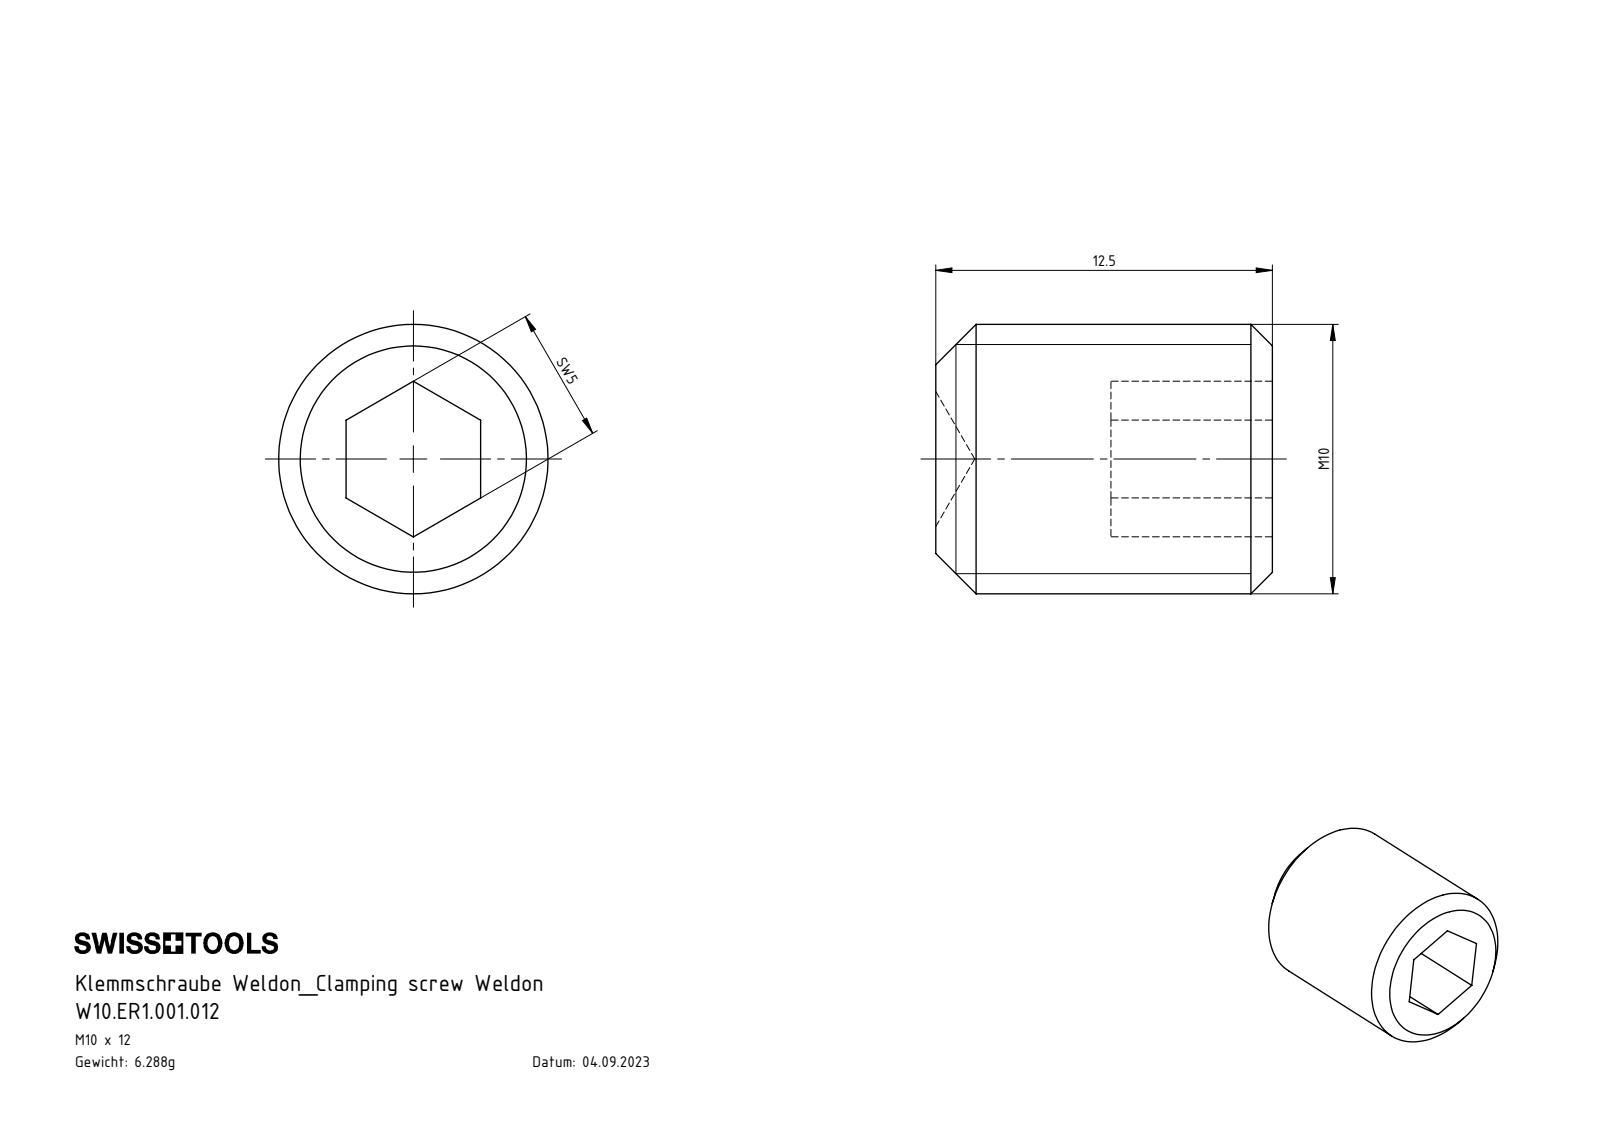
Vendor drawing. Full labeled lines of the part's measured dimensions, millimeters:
Part name (STEP PRODUCT): W10.ER1.001.012
STEP written by: SolidWorks 2017 (AUTOMOTIVE_DESIGN)
Units: millimetres
Bodies: 1 solid, 17 faces (9 planar, 2 cylindrical, 6 other)
Overall size (bounding box): 12.5 × 10 × 10
Volume: 801 mm³ · Surface area: 611 mm²
Round bosses / shafts (diameter × count): ⌀10 ×1
Main face-to-face distances: 5, 6, 12.5, 6.5
